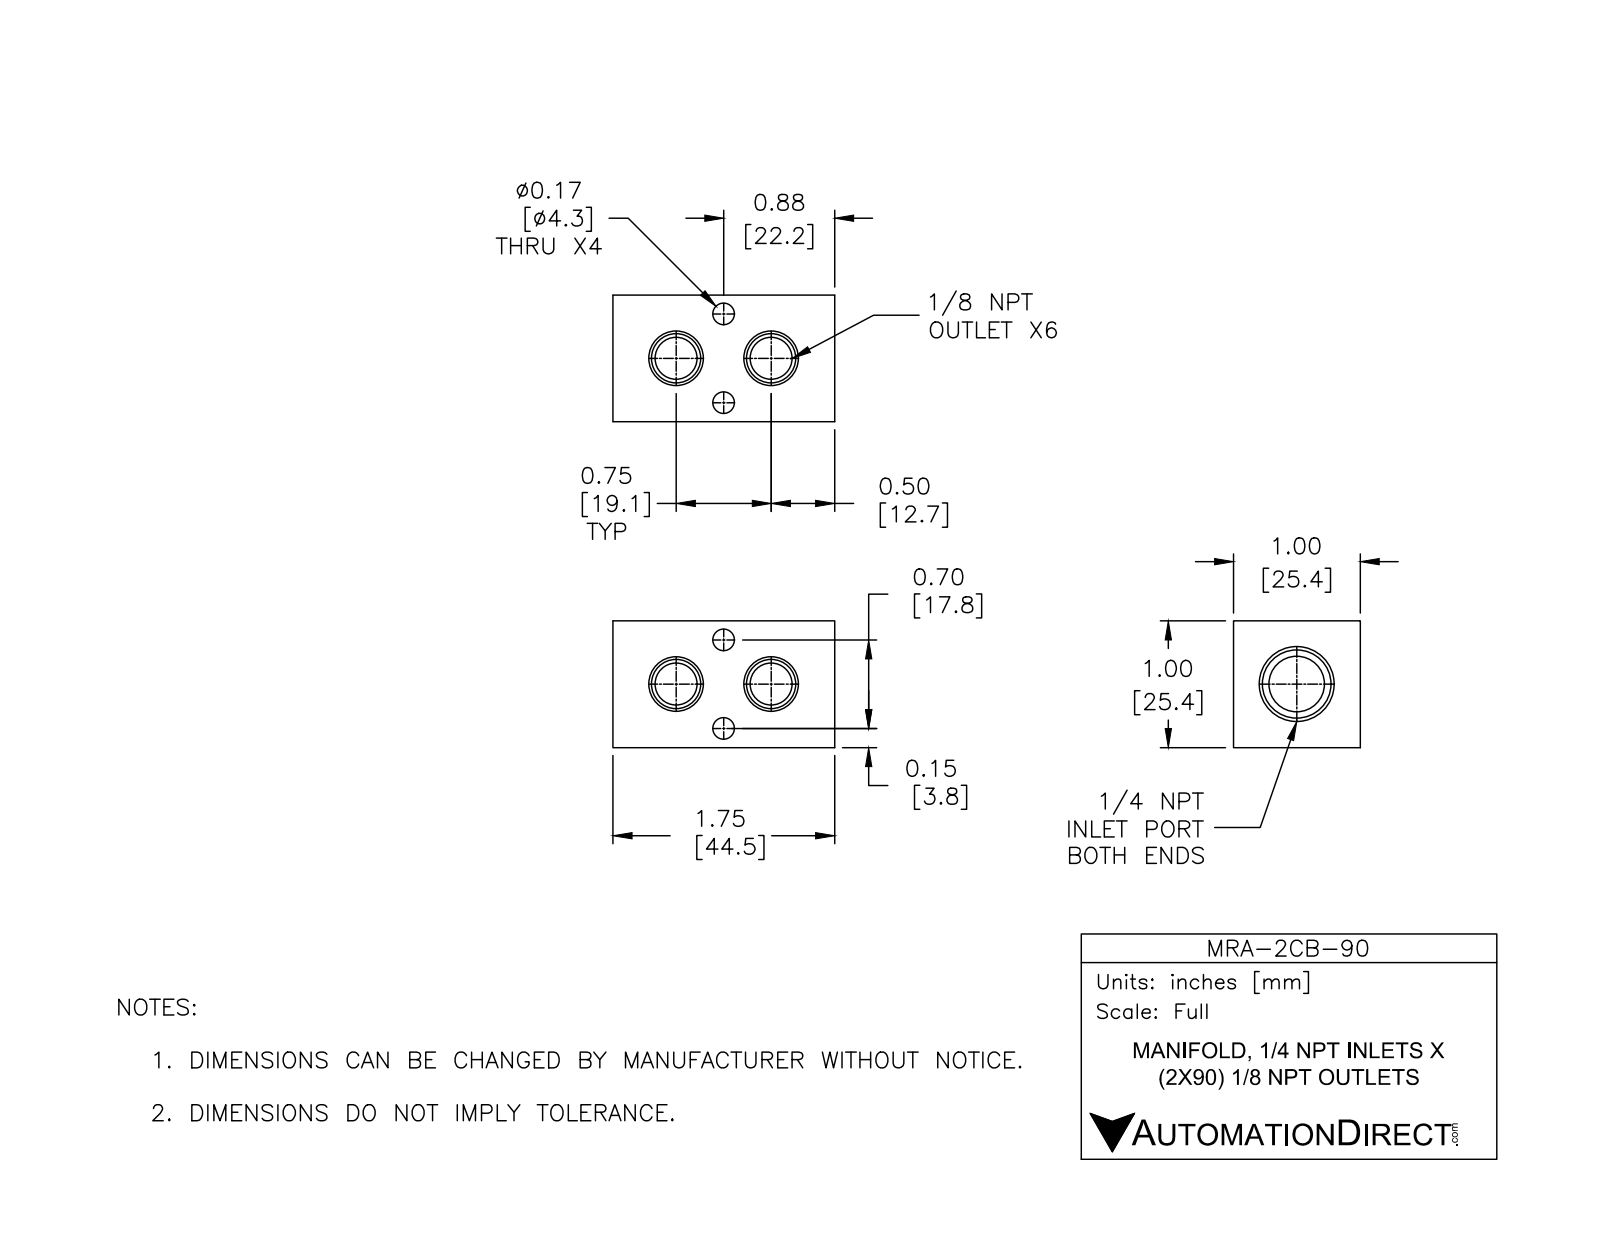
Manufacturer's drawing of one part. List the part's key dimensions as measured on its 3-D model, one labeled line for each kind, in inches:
Part name (STEP PRODUCT): MRA-2CB-90
STEP written by: SolidWorks 2015 (CONFIG_CONTROL_DESIGN)
Units: inches
Bodies: 1 solid, 72 faces (14 planar, 34 cylindrical, 24 other)
Overall size (bounding box): 1.75 × 1 × 1
Volume: 1.211 in³ · Surface area: 13.33 in²
Round holes (diameter × count): ⌀0.17 ×4, ⌀0.438 ×1
Partial cylindrical surfaces — rounded edges, fillets, slot ends (radius × count): R0.166 ×4
Main face-to-face distances: 1, 1.75, 0.27, 0.73, 0.39, 1.36, 0.97
Hole centre spacings: 0.7
